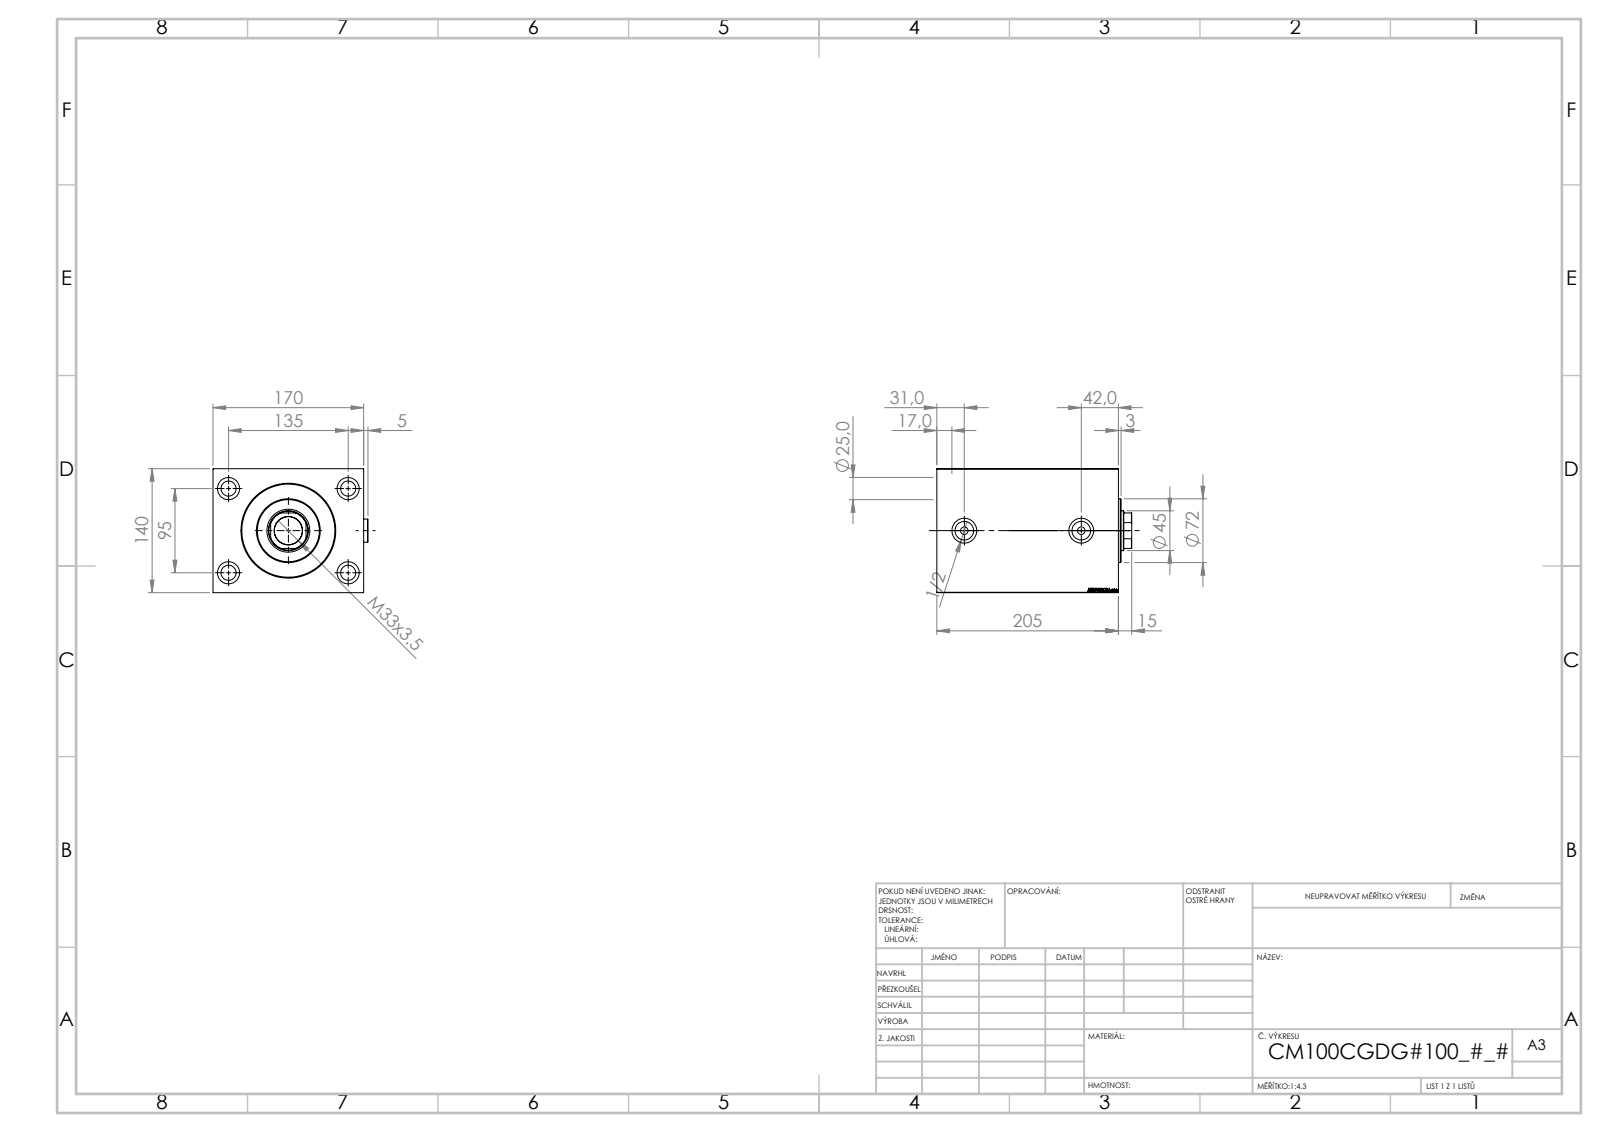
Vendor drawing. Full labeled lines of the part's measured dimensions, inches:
Part name (STEP PRODUCT): Zatka_OIL_PORT; V450CM_VC_B; V450CM_C_Body; V450CM_C_VCP
STEP written by: SolidWorks 2019 (CONFIG_CONTROL_DESIGN)
Units: inches
Bodies: 5 solids, 919 faces (443 planar, 78 cylindrical, 398 other)
Overall size (bounding box): 8.661 × 6.886 × 5.512
Volume: 244.6 in³ · Surface area: 565.2 in²
Round holes (diameter × count): ⌀0.669 ×4, ⌀0.984 ×4, ⌀0.335 ×2, ⌀0.825 ×2, ⌀1.102 ×2, ⌀1.24 ×1, ⌀1.772 ×1, ⌀1.909 ×1, ⌀3.937 ×1, ⌀4.016 ×1, ⌀4.134 ×1
Round bosses / shafts (diameter × count): ⌀1.024 ×2, ⌀2.835 ×1
Partial cylindrical surfaces — rounded edges, fillets, slot ends (radius × count): R0.866 ×1
Main face-to-face distances: 5.512, 6.693, 8.071, 7.047, 1.024, 0.591, 6.457, 7.48, 3.543, 3.937
Hole centre spacings: 3.25, 3.74, 5.315, 6.499, 5.197
